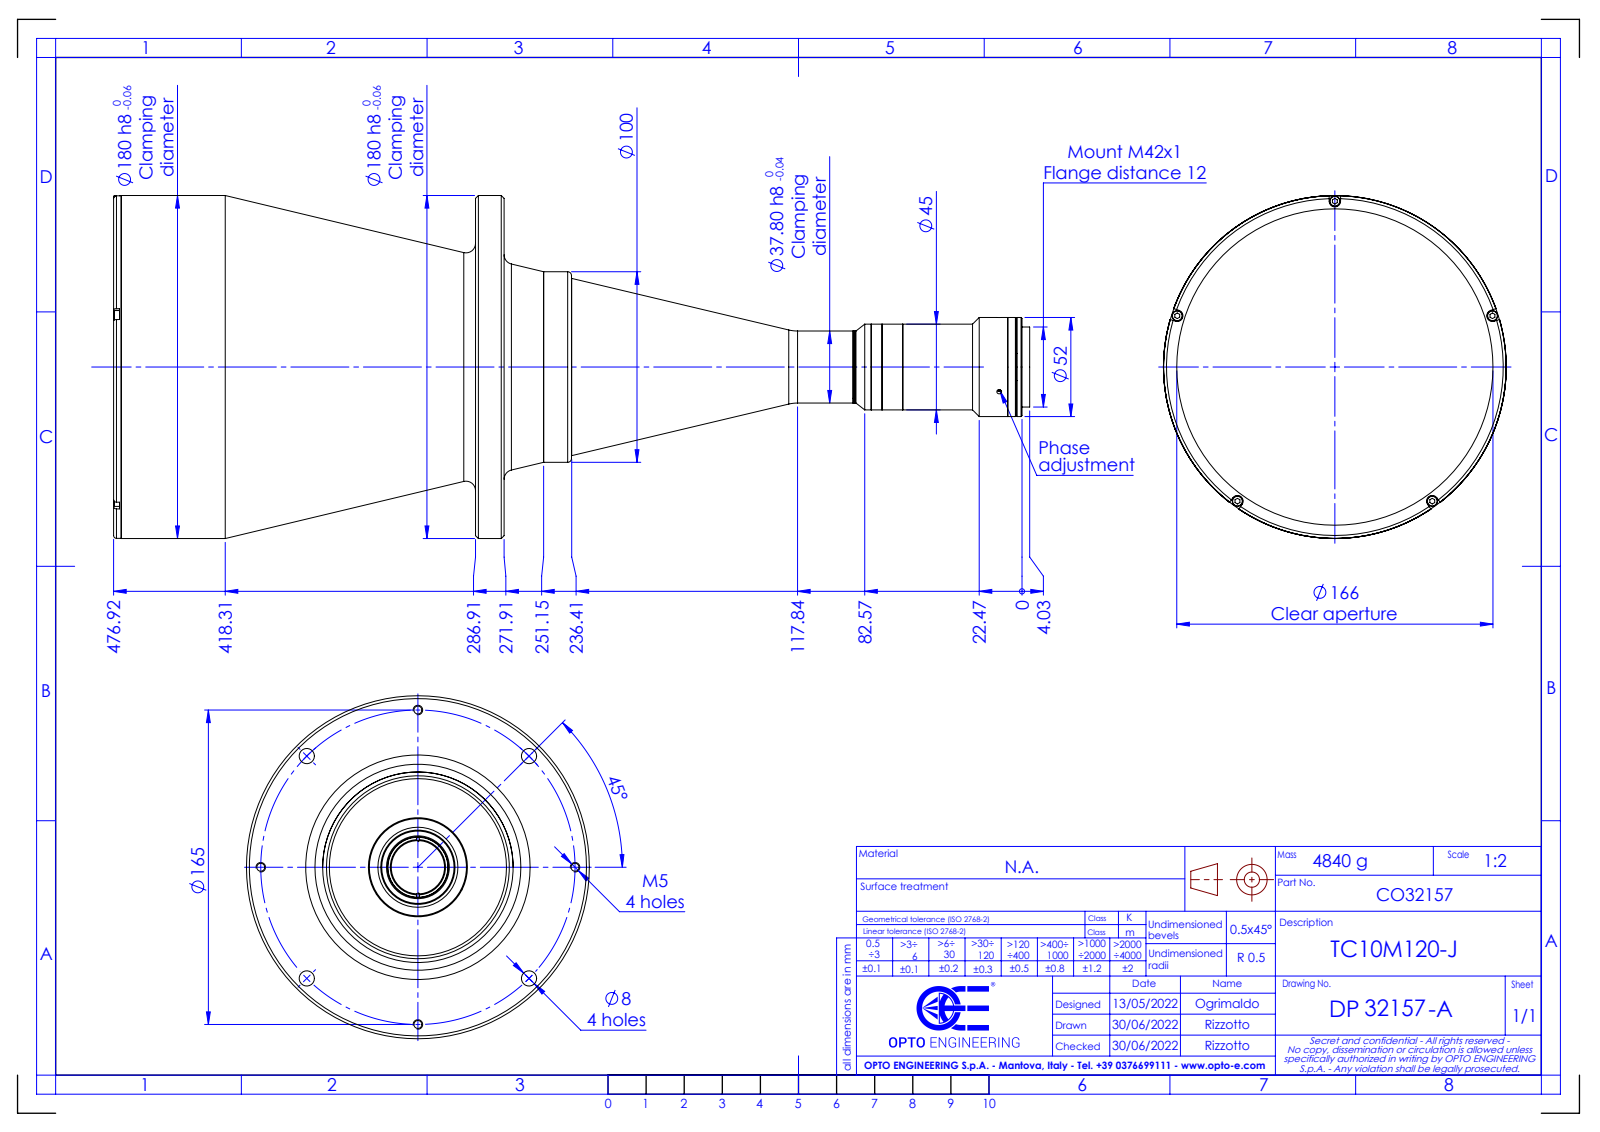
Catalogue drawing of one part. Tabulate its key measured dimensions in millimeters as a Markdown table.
| quantity | value |
| --- | --- |
| part name | DP32157-A_TC10M120-J |
| STEP written by | SolidWorks 2021 (CONFIG_CONTROL_DESIGN) |
| units | millimeters |
| bodies | 0 solids, 172 faces (47 planar, 82 cylindrical, 43 other) |
| overall size | 480.94 × 180 × 180 |
| round holes (diameter × count) | 4.2 × 4, 8 × 4, 2.5 × 3, 38 × 1, 41 × 1, 166 × 1, 170.8 × 1 |
| round bosses / shafts (diameter × count) | 5.5 × 5, 180 × 1, 179.8 × 1, 100 × 1, 93 × 1, 52 × 1, 51.8 × 1, 45 × 1 |
| partial cylindrical surfaces (radius × count) | 3 × 3 |
| main face-to-face distances | 15, 190.01, 205.01, 4, 186.01, 201.01, 225.77, 221.77, 35.76, 20.76 |
| hole center spacings | 63.14, 152.44, 82.5, 82.51, 116.67, 116.68, 165, 165.01 |
